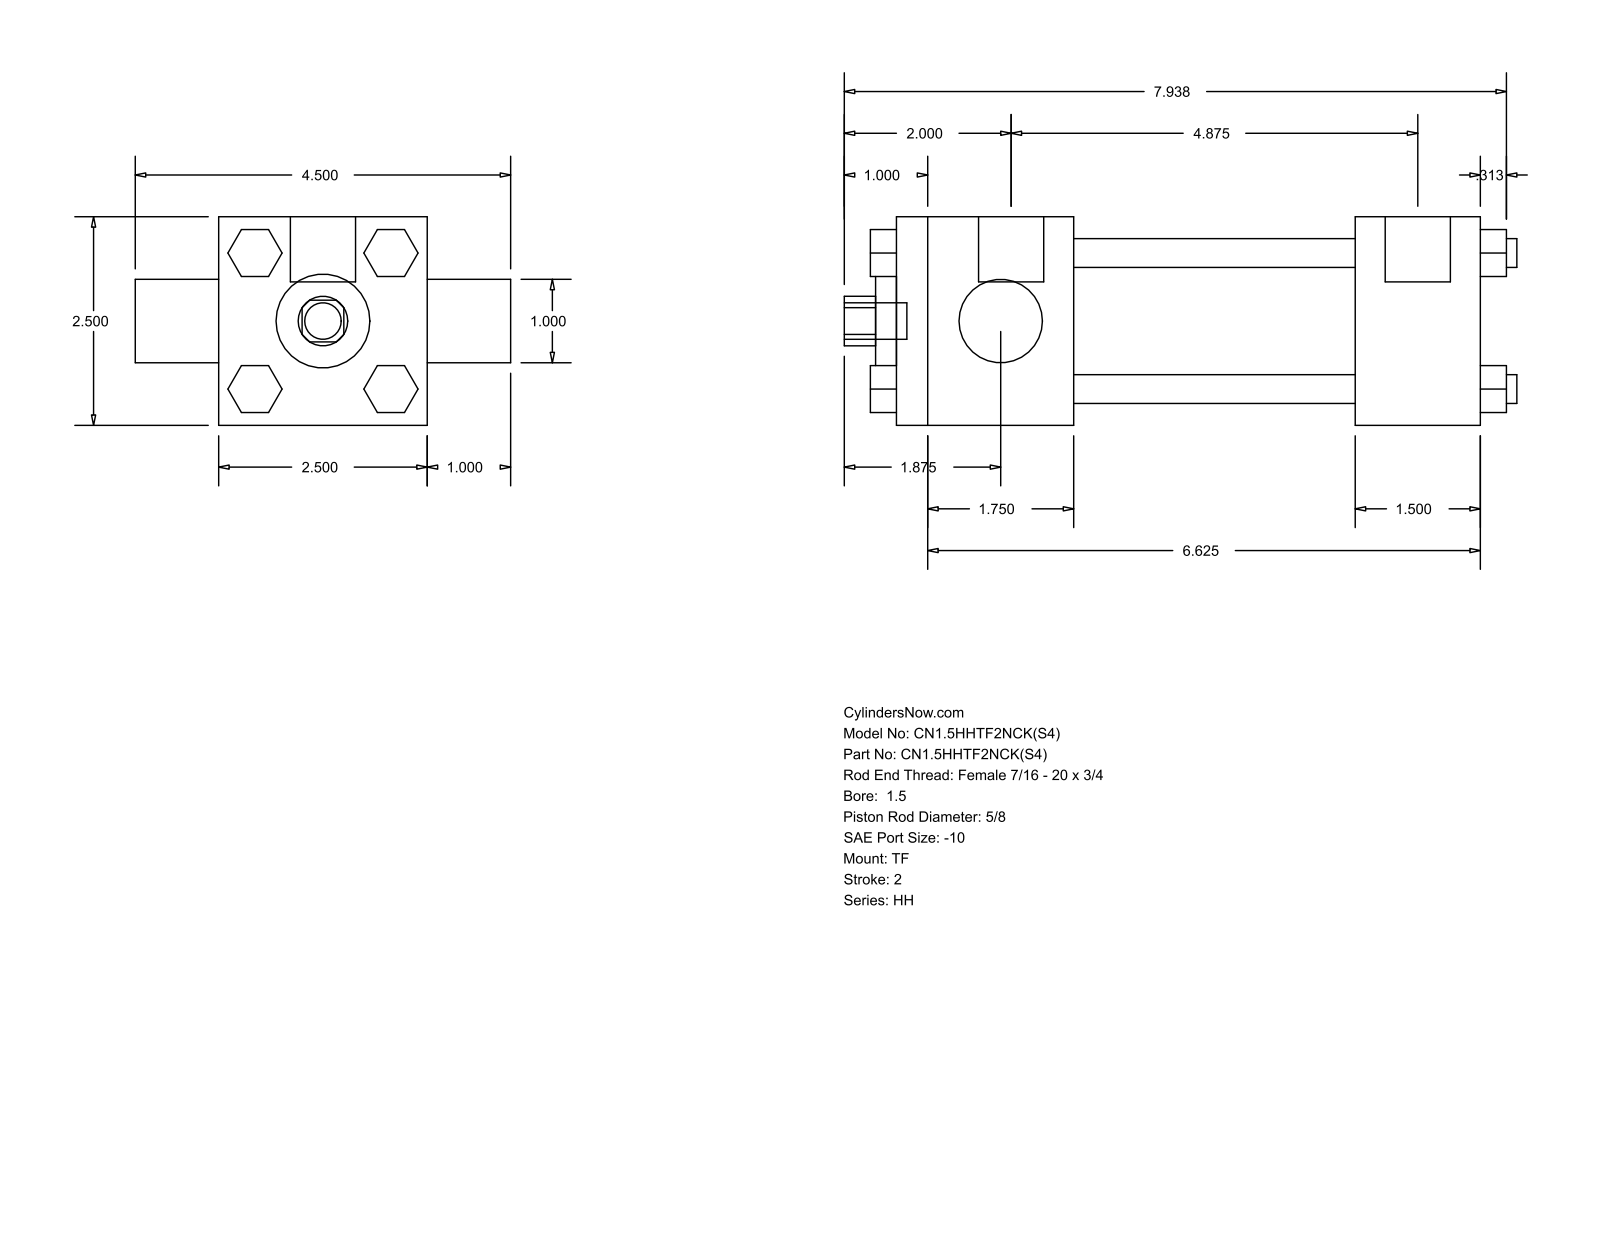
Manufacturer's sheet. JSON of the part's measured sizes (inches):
{"part_name": "HH_TF__0150_0.625", "step_written_by": "GSSL Pune (CONFIG_CONTROL_DESIGN)", "units": "inches", "bodies": {"solids": 0, "faces": 120, "planar": 92, "cylindrical": 28, "other": 0}, "overall_size": [8.063, 4.5, 2.5], "round_holes": [[0.625, 1], [1, 1], [1.125, 1], [1.75, 1]], "round_bosses_or_shafts": [[0.345, 4], [0.219, 3], [0.781, 2], [0.437, 1]], "partial_cylinders_radius": [[0.297, 1]], "face_to_face_distances": [2.5, 7, 2.125, 4.875, 5.5, 3.375, 1.5, 1, 0.815, 0.563]}
